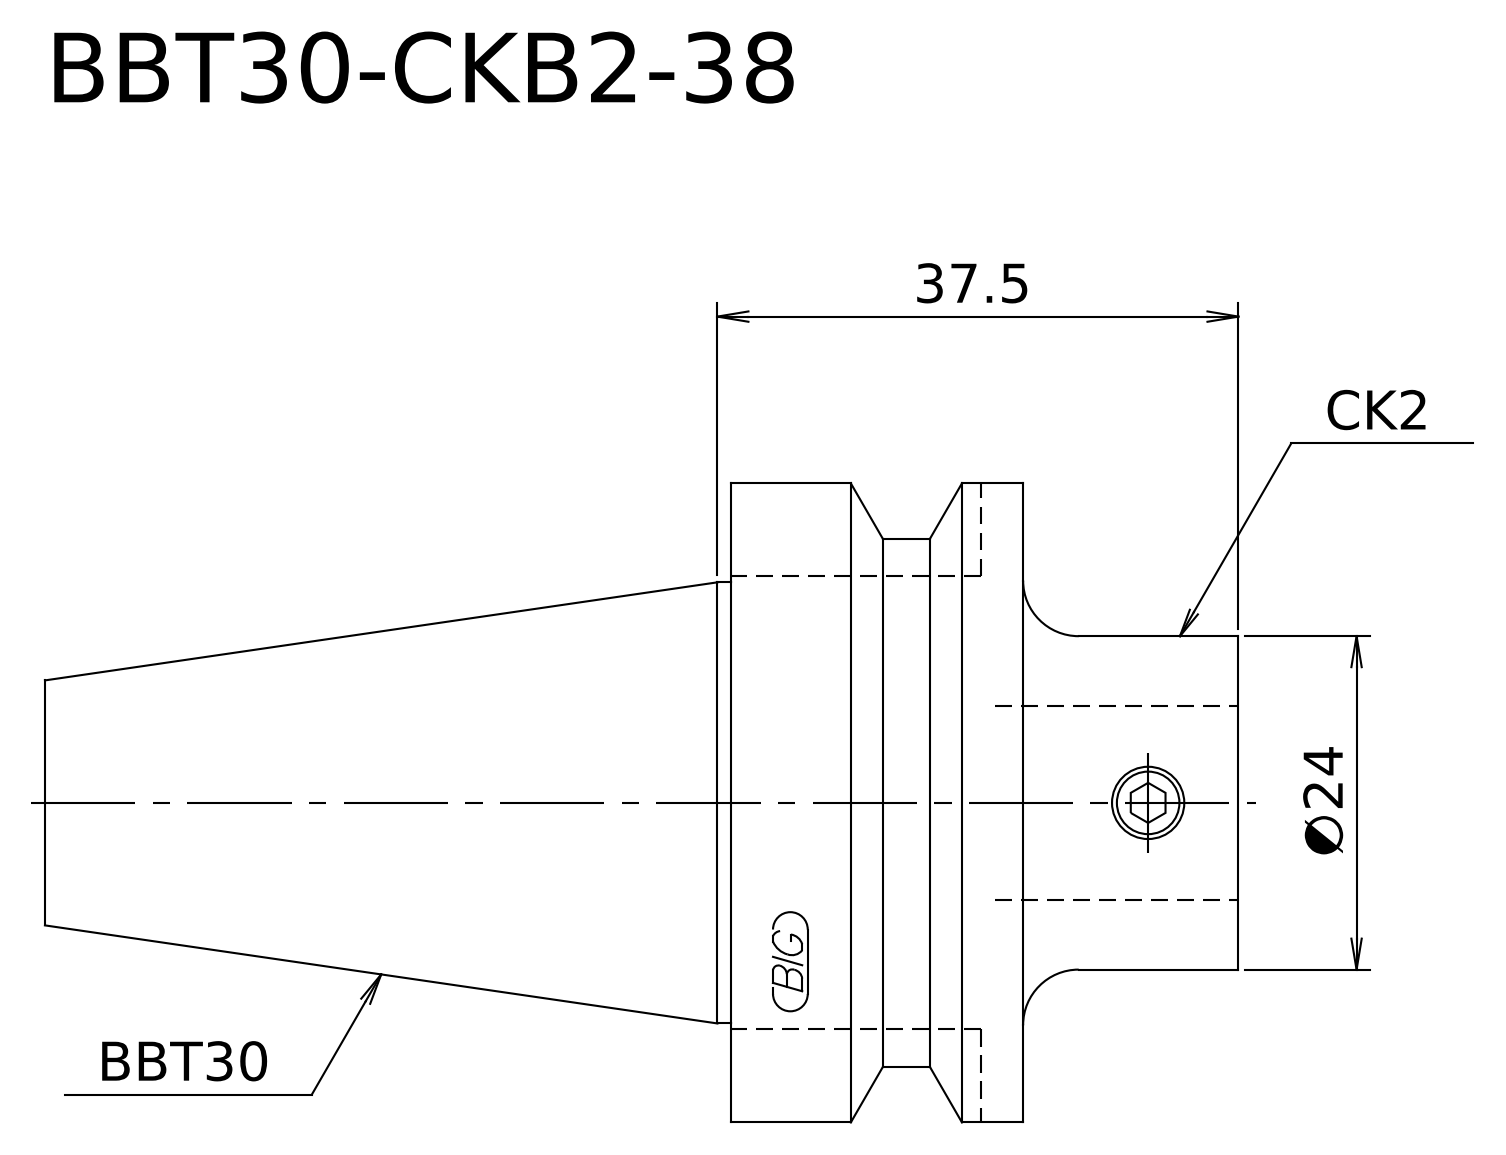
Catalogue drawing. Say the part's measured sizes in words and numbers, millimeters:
Its 3-D file was written by "Kubotek KeyCreator V8.5.1 (14335) (CONFIG_CONTROL_DESIGN)". It is 1 solid with 13 faces: 4 planar, 5 cylindrical and 4 other. Overall it measures 85.9 by 46 by 46 millimeters. Its volume is 64 542 cubic millimeters and its surface area 11 152 square millimeters. Round bosses or shafts: 1 of diameter 46, 1 of diameter 38, 1 of diameter 31.75, 1 of diameter 24. The main face-to-face distances are 21, 15.5, 36.5, 85.9, 70.4, 49.4.
